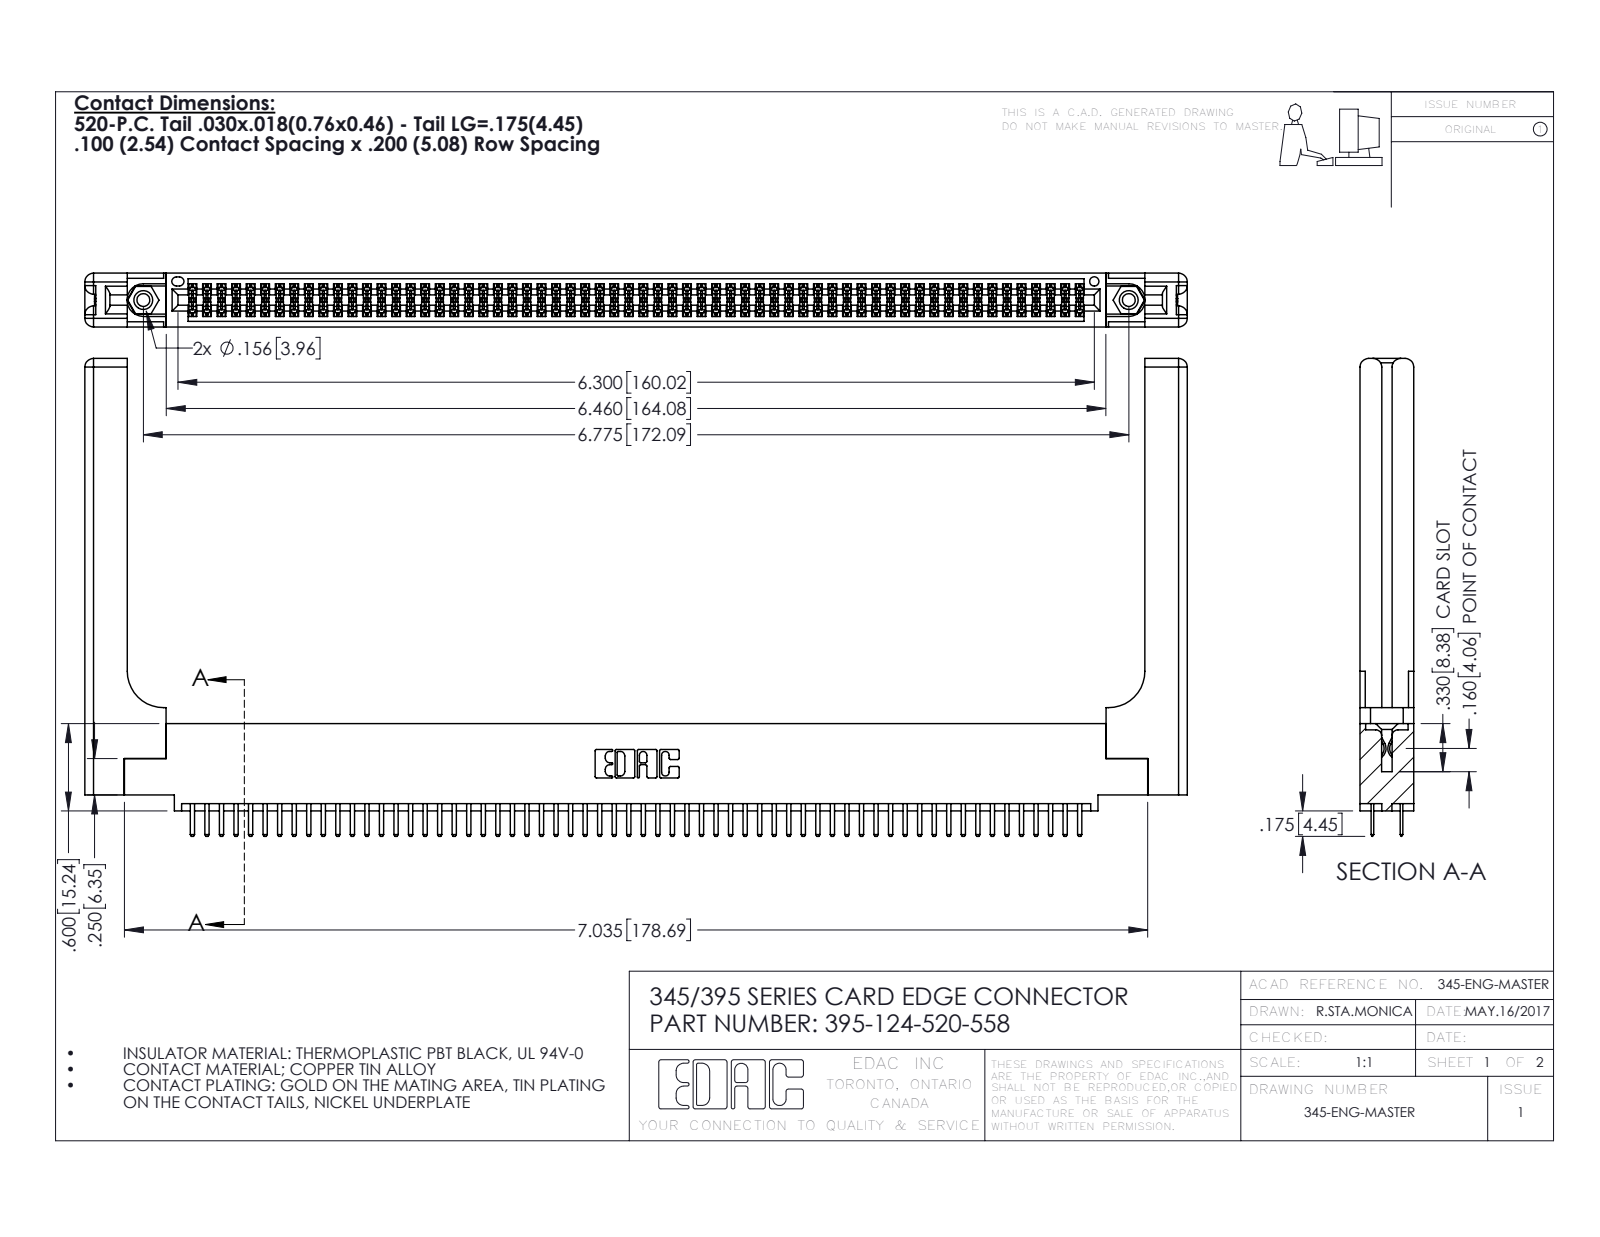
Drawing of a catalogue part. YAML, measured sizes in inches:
part_name: "345-292-001_345-293-120; 395-124-520-558; 345-220-058_345-220-058; 345-250-001_345-250-001-102 (+1 more)"
step_written_by: "SolidWorks 2016 (CONFIG_CONTROL_DESIGN)"
units: inches
bodies: {solids: 129, faces: 7082, planar: 4572, cylindrical: 2450, other: 60}
overall_size: [7.579, 3.285, 0.37]
volume: 1.662
surface_area: 51.38
round_holes:
  - {diameter: 0.089, count: 2}
  - {diameter: 0.125, count: 2}
  - {diameter: 0.156, count: 2}
  - {diameter: 0.064, count: 1}
round_bosses_or_shafts:
  - {diameter: 0.155, count: 2}
partial_cylinders:
  - {radius: 0.006, count: 186}
  - {radius: 0.01, count: 128}
  - {radius: 0.01, count: 22}
  - {radius: 0.06, count: 16}
  - {radius: 0.007, count: 6}
  - {radius: 0.031, count: 6}
  - {radius: 0.026, count: 3}
  - {radius: 0.014, count: 2}
face_to_face_distances: [0.072, 0.298, 0.37, 0.2, 0.098, 0.272, 0.025, 0.225, 0.022, 0.072]
hole_center_spacings: [0.27, 6.539, 6.775]
